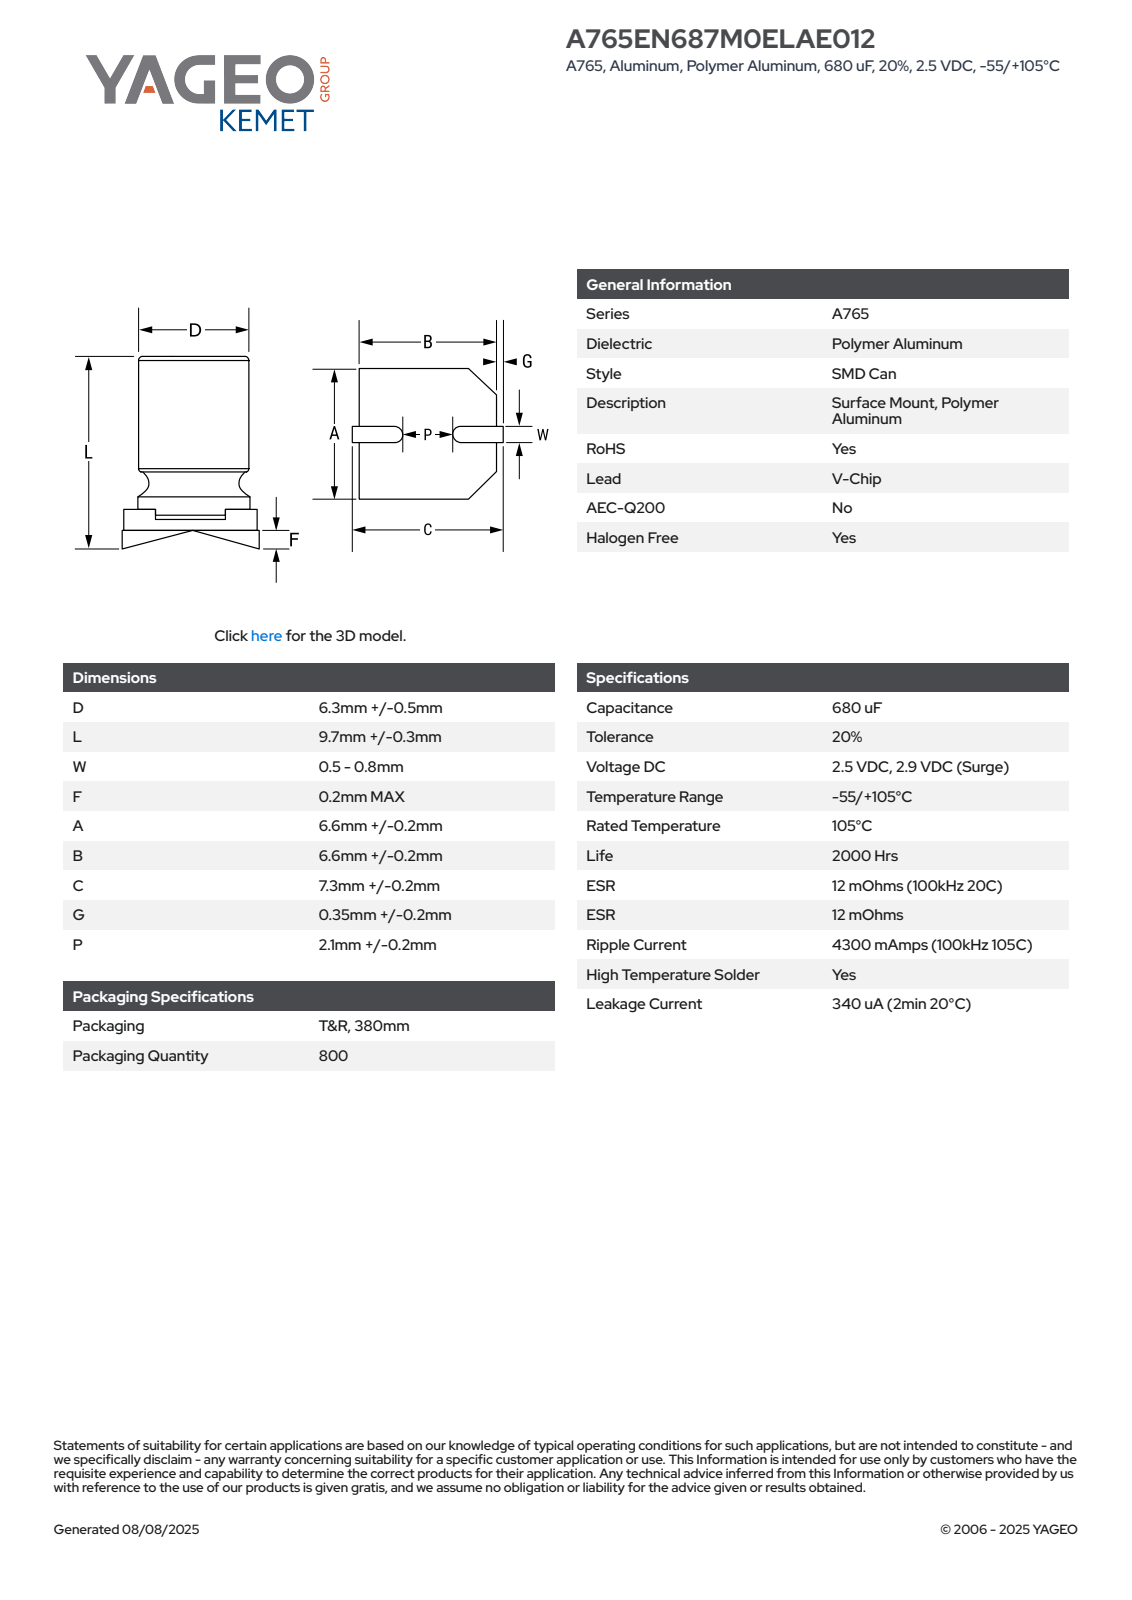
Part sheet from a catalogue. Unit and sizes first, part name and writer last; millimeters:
Units: millimetres
Overall size (bounding box): 10.01 × 7.5 × 6.8
Round bosses / shafts (diameter × count): ⌀6.5 ×1
Partial cylindrical surfaces — rounded edges, fillets, slot ends (radius × count): R0.2 ×2, R2.7 ×1, R3.4 ×1
Main face-to-face distances: 0.5, 9.8, 9.3, 9.81, 9.31, 6.8, 2, 2.5, 7.3, 7.31
Volume: 337 mm³ · Surface area: 409 mm²
Bodies: 5 solids, 76 faces (59 planar, 11 cylindrical, 6 other)
Part name (STEP PRODUCT): CAC_KS_6.3X9.7_D6.8L10W0.8F0.2A6.8B6.8C7.5P2.3
STEP written by: SolidWorks 2014 (AUTOMOTIVE_DESIGN)
